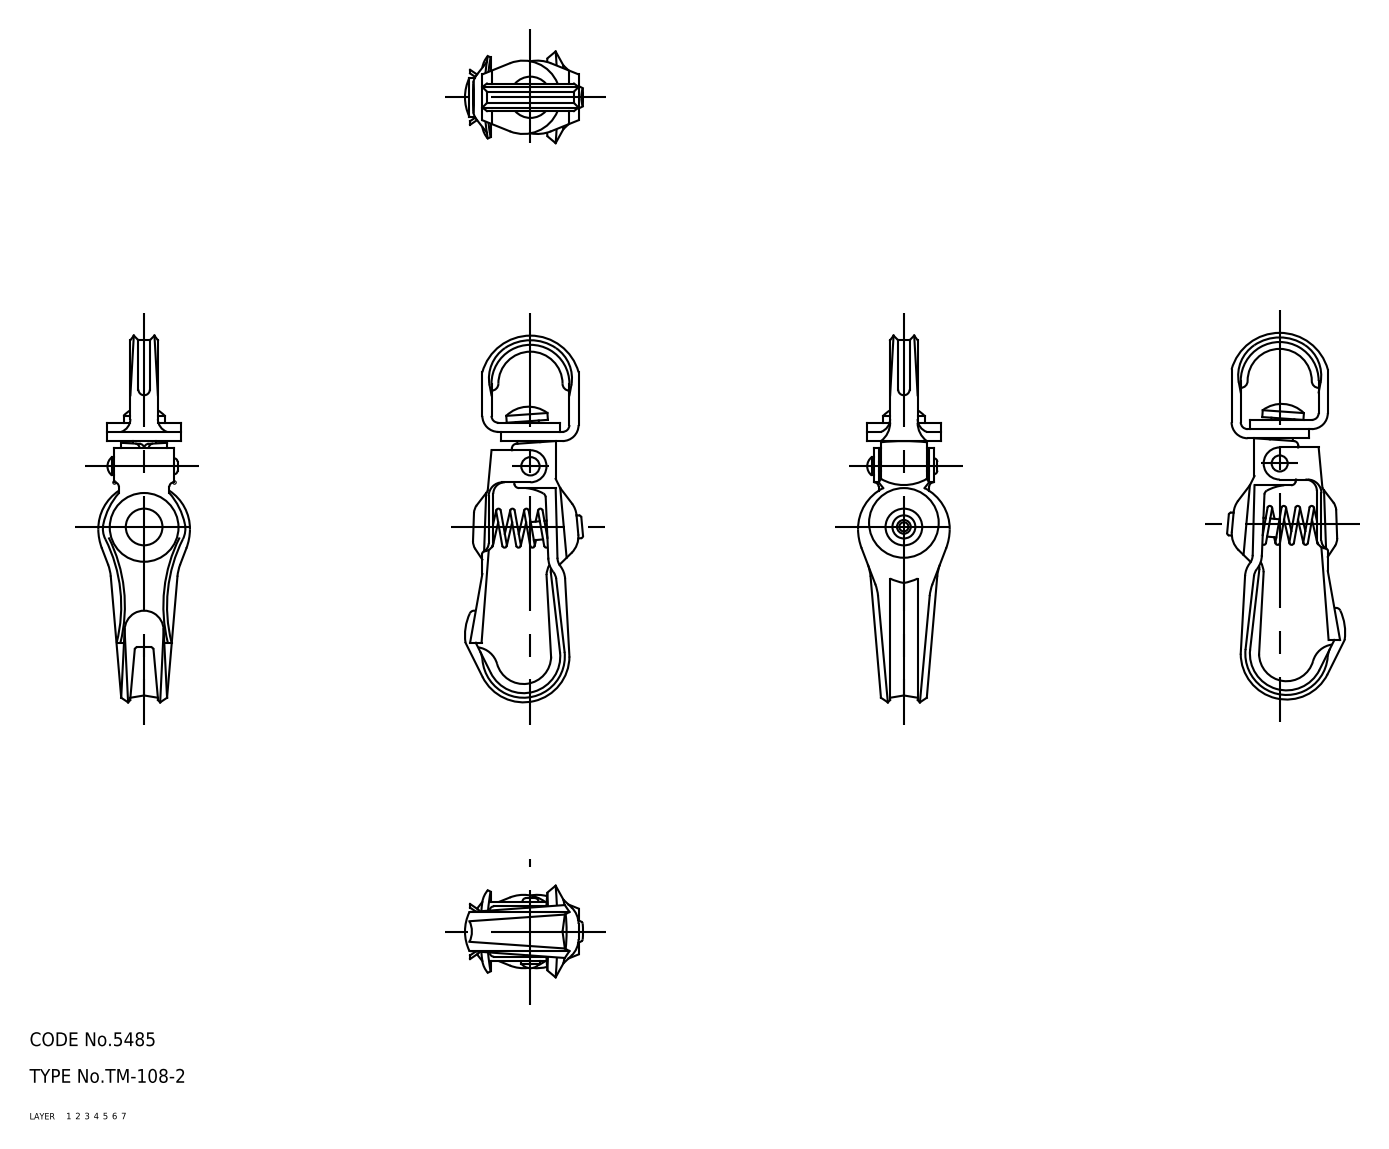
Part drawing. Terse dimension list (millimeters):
name: spring; pin_B; pin_A; stopper (+4 more)
written by: CADfix (AUTOMOTIVE_DESIGN)
unit: mm
bodies: 7 solids, 225 faces (0 planar, 0 cylindrical, 225 other)
size: 80 × 25.76 × 20
volume: 5 458 mm³; area: 7 741 mm²
